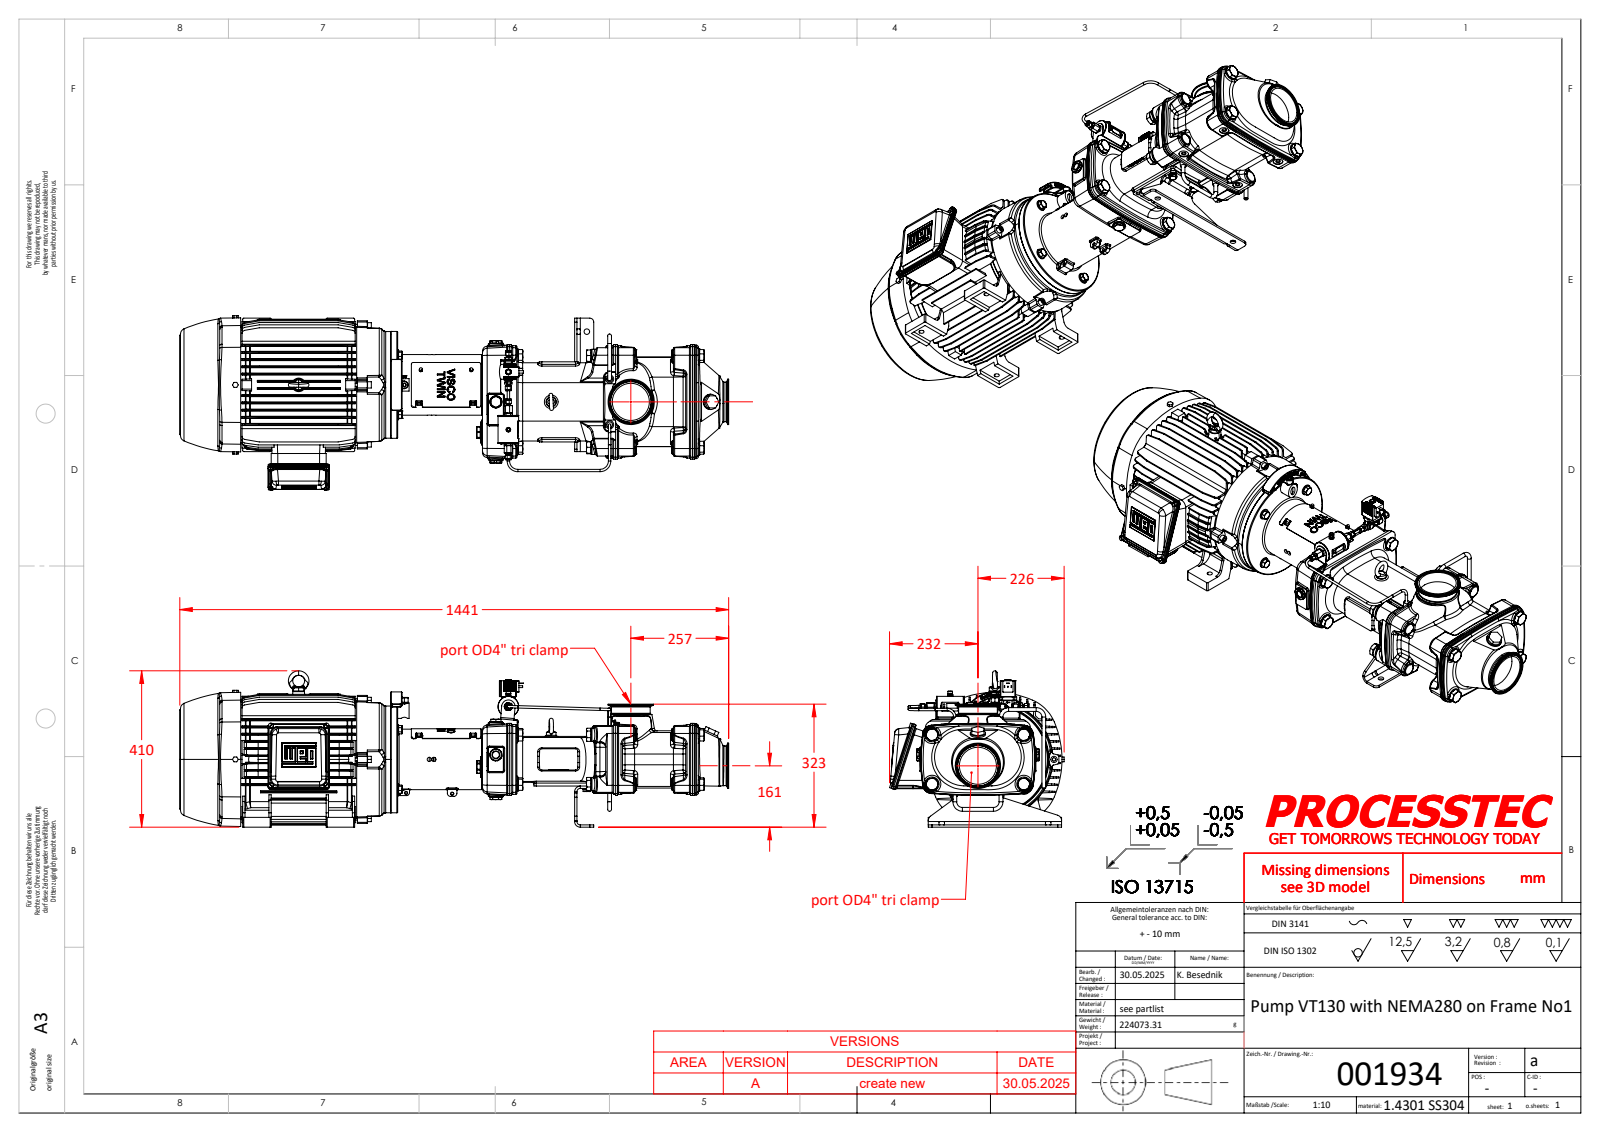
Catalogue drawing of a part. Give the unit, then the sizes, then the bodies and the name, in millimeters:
Units: millimetres
Overall size (bounding box): 1441 × 458.07 × 410.3
Round holes (diameter × count): ⌀8.5 ×10, ⌀17.5 ×9, ⌀6.8 ×8, ⌀10.5 ×8, ⌀17 ×8, ⌀8 ×7, ⌀8.2 ×6, ⌀13.2 ×6, ⌀14 ×6, ⌀14.5 ×6, ⌀4.1 ×5, ⌀7.6 ×5
Round bosses / shafts (diameter × count): ⌀6 ×13, ⌀8 ×12, ⌀10 ×11, ⌀5 ×8, ⌀20 ×6, ⌀16 ×6, ⌀13.2 ×6, ⌀13 ×6
Partial cylindrical surfaces — rounded edges, fillets, slot ends (radius × count): R2 ×120, R3 ×107, R4 ×83, R0.5 ×60, R8 ×43, R1.5 ×33, R7 ×27, R6 ×21
Main face-to-face distances: 481, 189.19, 305, 786, 18.67, 132.27, 165.28, 5.24, 150.94, 170.52
Hole centre spacings: 51, 129.3, 55, 62.81, 113.29, 139.08, 168.03, 6.41
Volume: 70 620 000 mm³ · Surface area: 4 186 000 mm²
Bodies: 105 solids, 8933 faces (2959 planar, 2087 cylindrical, 3887 other)
Part name (STEP PRODUCT): 001094_ISO 4017 - M20 X 45 - A2-70; 001010; 001075; 001539 (+8 more)
STEP written by: SolidWorks 2023 (AUTOMOTIVE_DESIGN)
